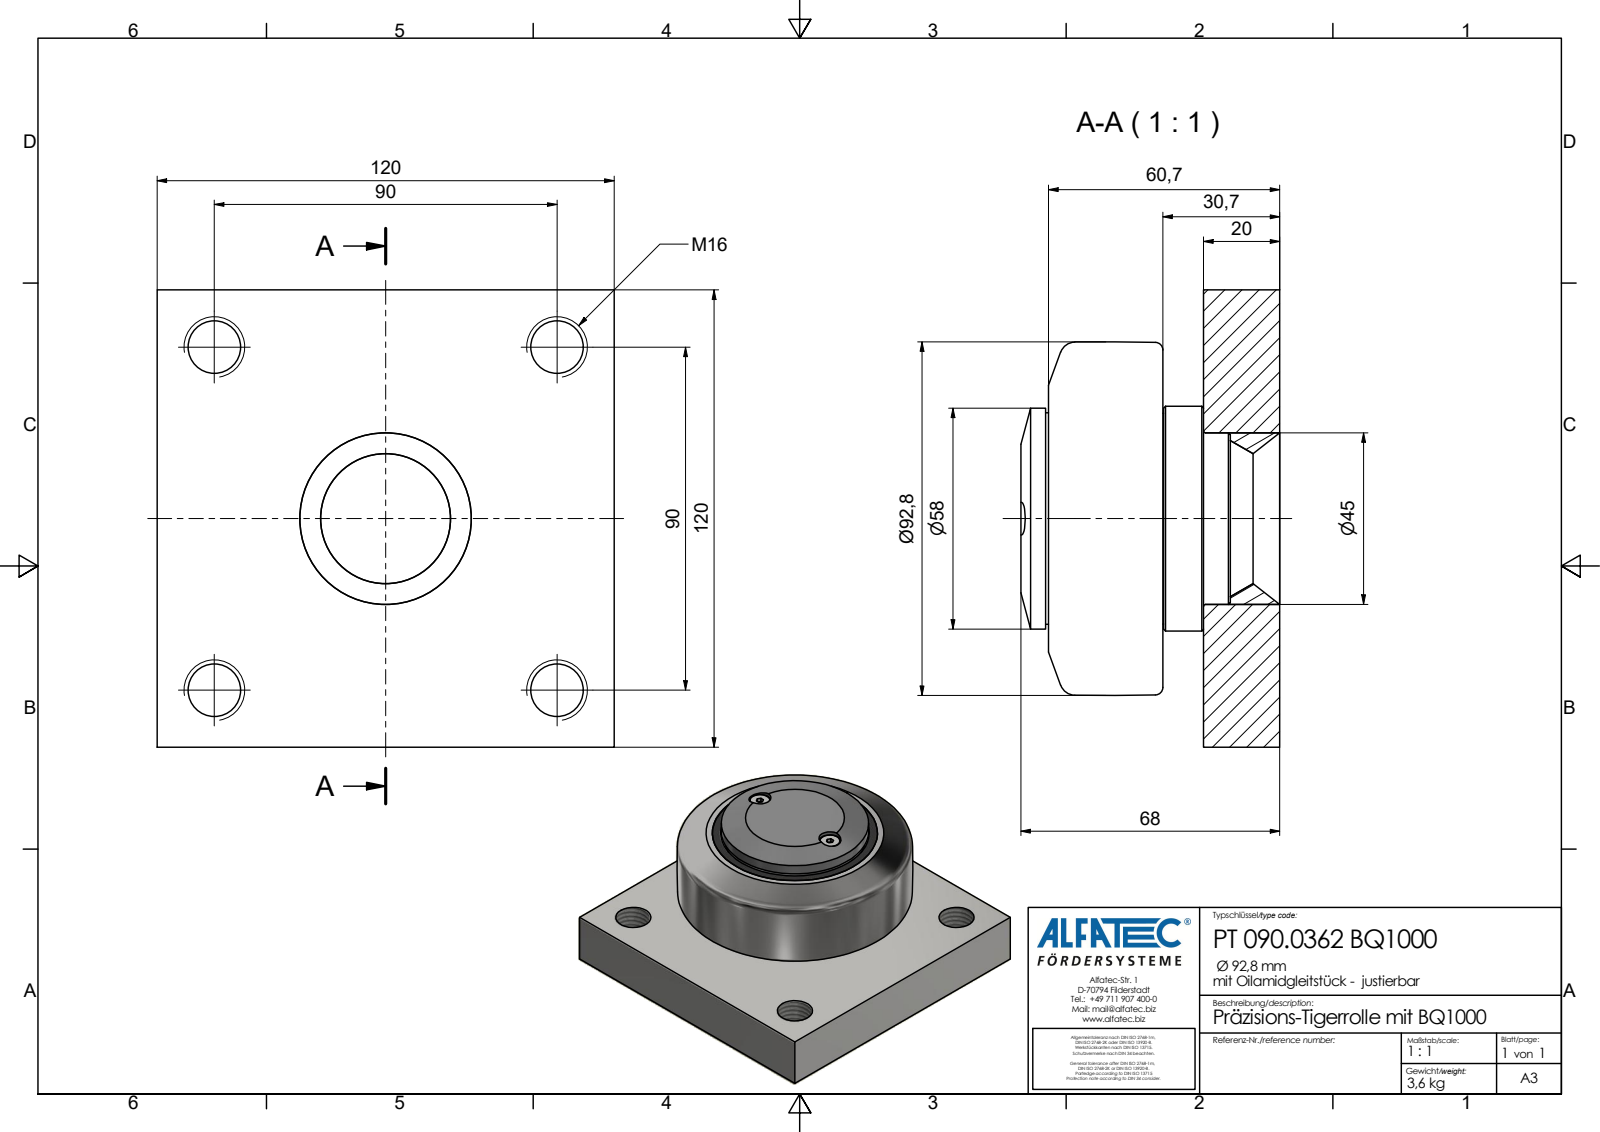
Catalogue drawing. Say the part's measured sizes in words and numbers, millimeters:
The part is named "PT 090.0362 BQ1000_Kontur". Its 3-D file was written by "Autodesk Inventor 2020 (AP242_MANAGED_MODEL_BASED_3D_ENGINEERING_MIM_LF)". It is 1 solid with 50 faces: 28 planar, 12 cylindrical and 10 other. Overall it measures 120 by 120 by 68 millimeters. Its volume is 509 102 cubic millimeters and its surface area 60 564 square millimeters. Round holes: 4 of diameter 13.84, 2 of diameter 8.6. Round bosses or shafts: 2 of diameter 7.8, 1 of diameter 59, 1 of diameter 58, 1 of diameter 55.5, 1 of diameter 55.3. The main face-to-face distances are 20, 120, 30.7, 10.7, 60.7, 40.7, 30, 68, 48, 37.3. The hole center spacings are 51.72, 78.65, 90, 127.28, 39.
